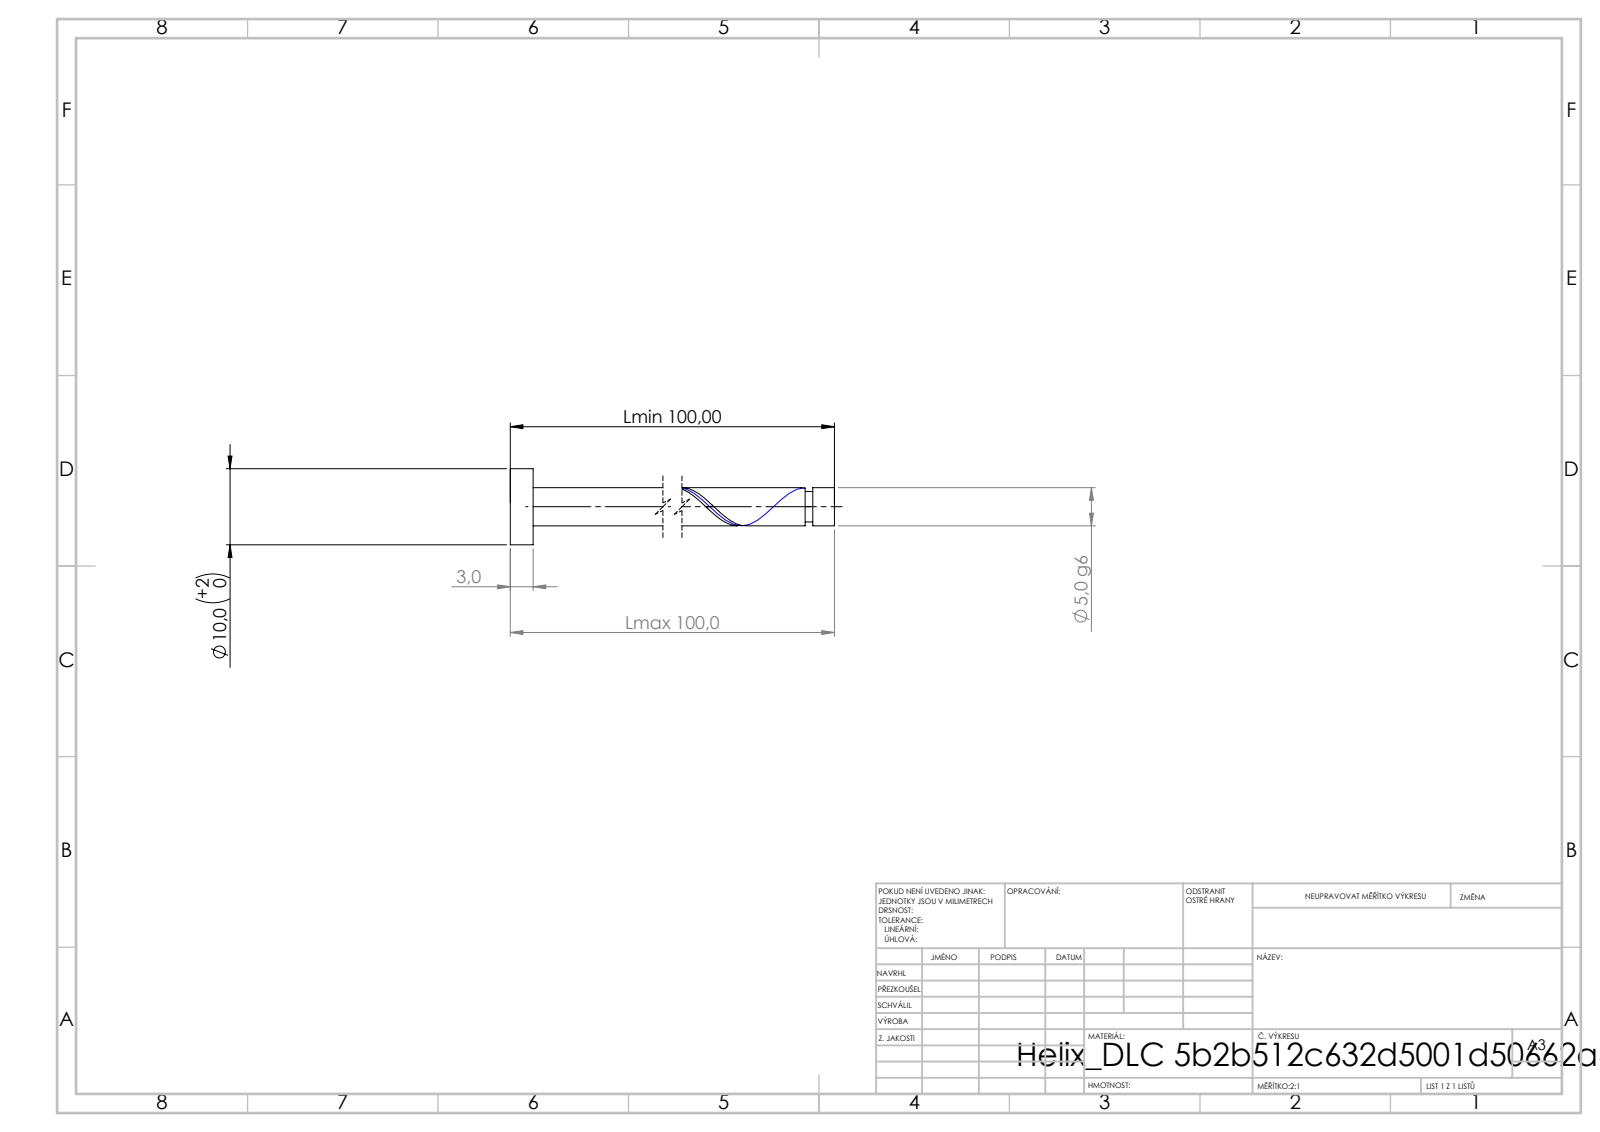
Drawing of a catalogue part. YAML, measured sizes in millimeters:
step_written_by: "SolidWorks 2019 (CONFIG_CONTROL_DESIGN)"
units: millimeters
bodies: {solids: 1, faces: 21, planar: 6, cylindrical: 14, other: 1}
overall_size: [100, 10, 10]
volume: 2114
surface_area: 1823
round_bosses_or_shafts:
  - {diameter: 10, count: 1}
  - {diameter: 5, count: 1}
  - {diameter: 4, count: 1}
face_to_face_distances: [3, 100, 97, 97.15, 94.15, 2.85, 96.15, 93.15, 1, 3.85]
